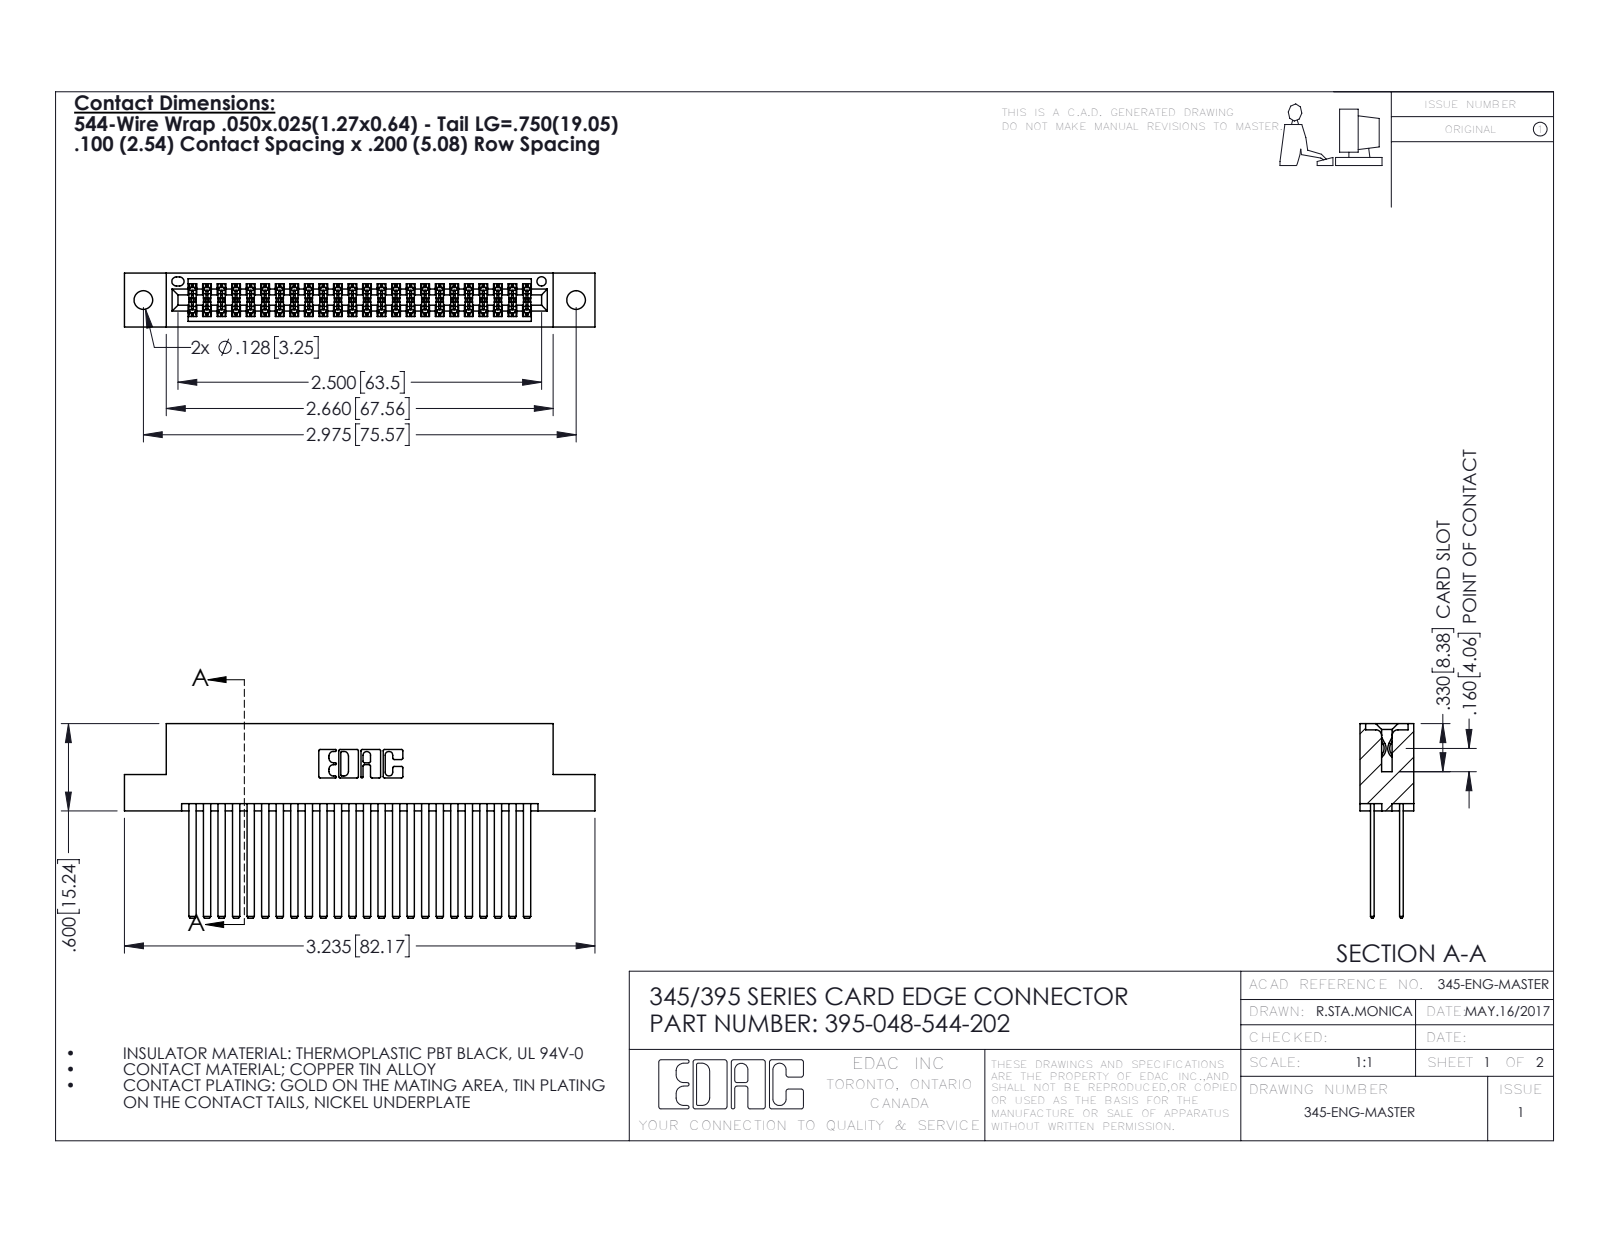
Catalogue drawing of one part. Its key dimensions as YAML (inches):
part_name: "345-292-001_345-293-144; 395-048-544-202; 345 Part_Flush Mounting Lugs - 0.128 Dia"
step_written_by: "SolidWorks 2016 (CONFIG_CONTROL_DESIGN)"
units: inches
bodies: {solids: 49, faces: 2238, planar: 1472, cylindrical: 766, other: 0}
overall_size: [3.235, 1.337, 0.37]
volume: 0.516
surface_area: 21.46
round_holes:
  - {diameter: 0.128, count: 2}
  - {diameter: 0.064, count: 1}
partial_cylinders:
  - {radius: 0.006, count: 72}
  - {radius: 0.01, count: 22}
  - {radius: 0.007, count: 6}
  - {radius: 0.031, count: 6}
  - {radius: 0.026, count: 3}
  - {radius: 0.014, count: 2}
  - {radius: 0.019, count: 2}
  - {radius: 0.022, count: 2}
face_to_face_distances: [0.2, 0.298, 0.072, 0.098, 0.272, 0.025, 0.225, 0.37, 0.175, 0.05]
hole_center_spacings: [0.27, 2.741, 2.975]
